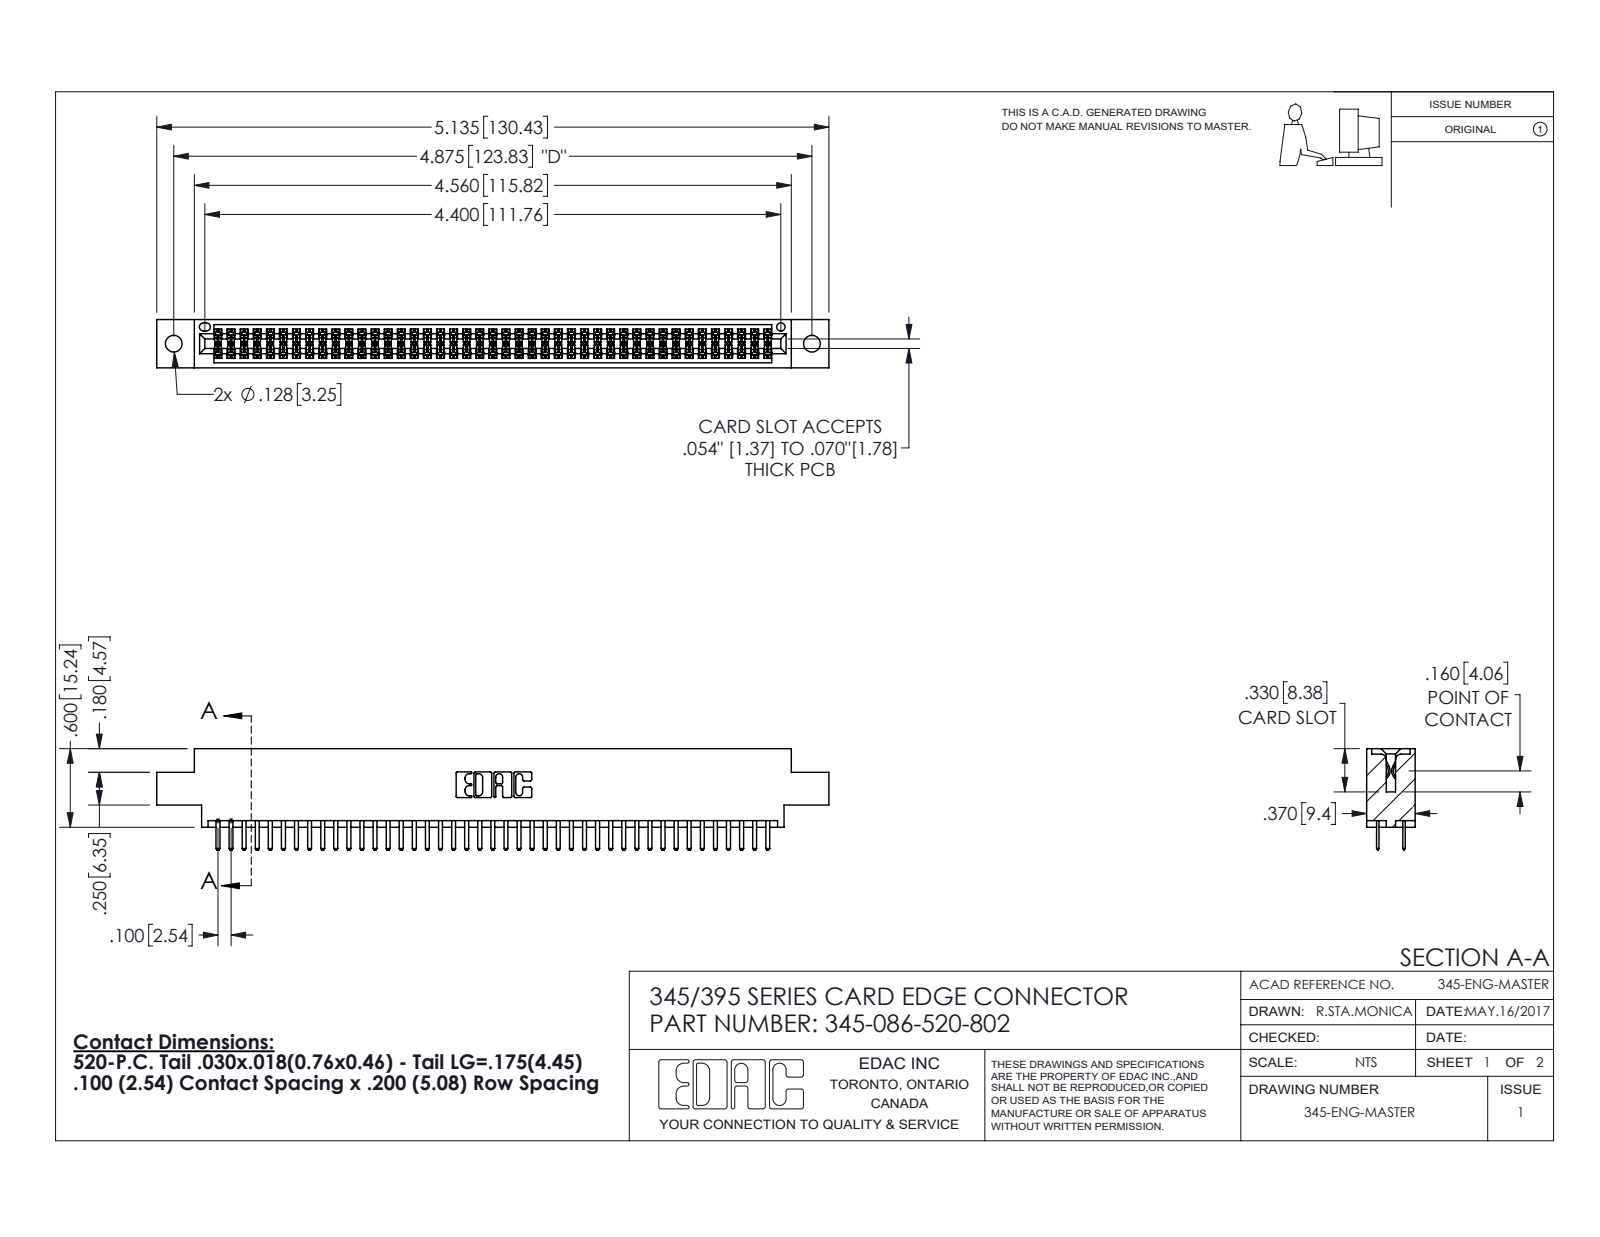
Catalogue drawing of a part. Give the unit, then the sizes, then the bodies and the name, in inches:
Units: inches
Overall size (bounding box): 5.135 × 0.775 × 0.37
Round holes (diameter × count): ⌀0.128 ×2, ⌀0.064 ×1
Partial cylindrical surfaces — rounded edges, fillets, slot ends (radius × count): R0.006 ×129, R0.01 ×90, R0.01 ×22, R0.007 ×6, R0.031 ×6, R0.026 ×3, R0.014 ×2, R0.019 ×2
Main face-to-face distances: 0.072, 0.298, 0.2, 0.37, 0.098, 0.272, 0.025, 0.225, 0.022, 0.175
Hole centre spacings: 0.27, 4.639, 4.875
Volume: 0.762 in³ · Surface area: 28.32 in²
Bodies: 87 solids, 4774 faces (3094 planar, 1680 cylindrical, 0 other)
Part name (STEP PRODUCT): 345-086-520-802; 345 Part_0.170 Offset - 0.128 Dia; 345-292-001_345-293-120
STEP written by: SolidWorks 2016 (CONFIG_CONTROL_DESIGN)
